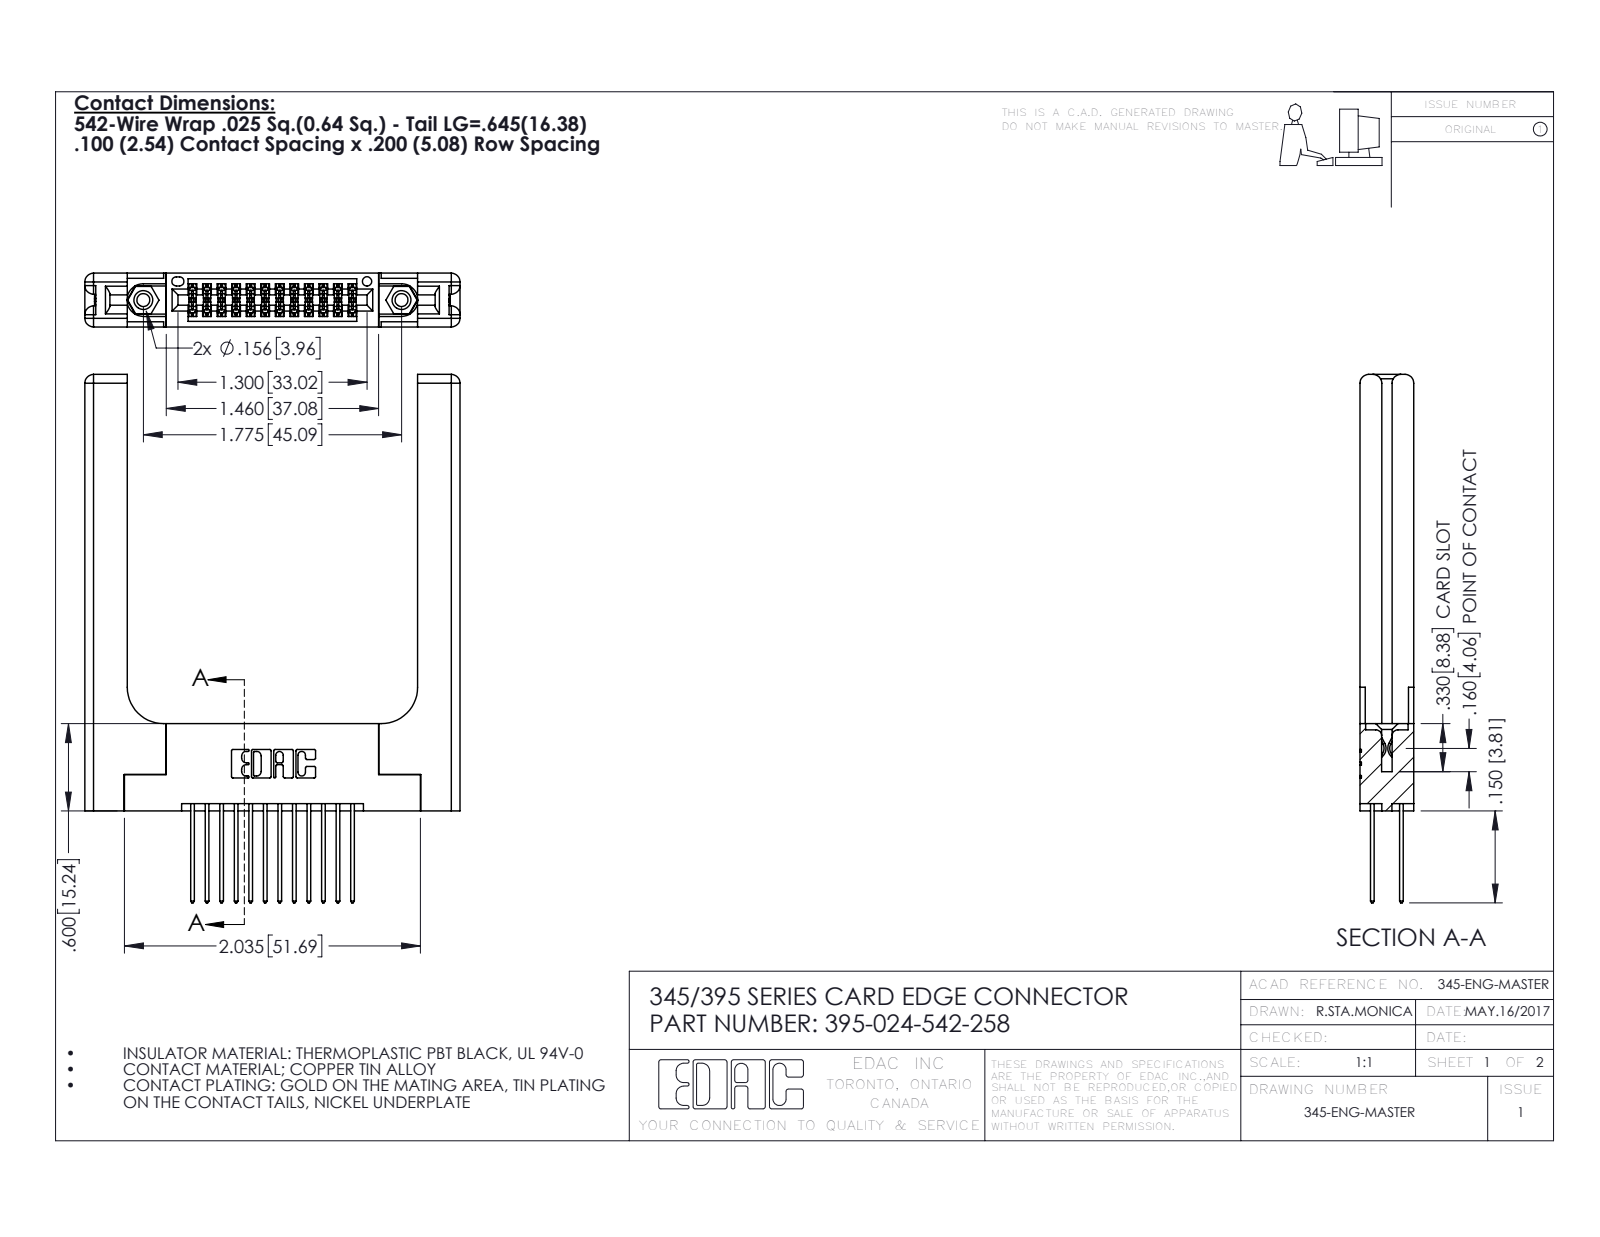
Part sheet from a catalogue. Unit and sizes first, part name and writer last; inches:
Units: inches
Overall size (bounding box): 3.632 × 2.579 × 0.37
Round holes (diameter × count): ⌀0.089 ×2, ⌀0.125 ×2, ⌀0.156 ×2, ⌀0.064 ×1
Round bosses / shafts (diameter × count): ⌀0.155 ×2
Partial cylindrical surfaces — rounded edges, fillets, slot ends (radius × count): R0.006 ×36, R0.01 ×24, R0.01 ×22, R0.06 ×16, R0.007 ×6, R0.031 ×6, R0.026 ×3, R0.014 ×2
Main face-to-face distances: 0.37, 0.072, 0.298, 0.2, 0.077, 0.148, 0.15, 0.22, 0.098, 0.272
Hole centre spacings: 0.27, 1.543, 1.775
Volume: 0.895 in³ · Surface area: 21.95 in²
Bodies: 29 solids, 1582 faces (1020 planar, 502 cylindrical, 60 other)
Part name (STEP PRODUCT): 345 Part_Flush Mounting Lugs - 0.156 Dia-TH; 345-220-058_345-220-058; 345-292-001_345-293-142; 395-024-542-258 (+1 more)
STEP written by: SolidWorks 2016 (CONFIG_CONTROL_DESIGN)
